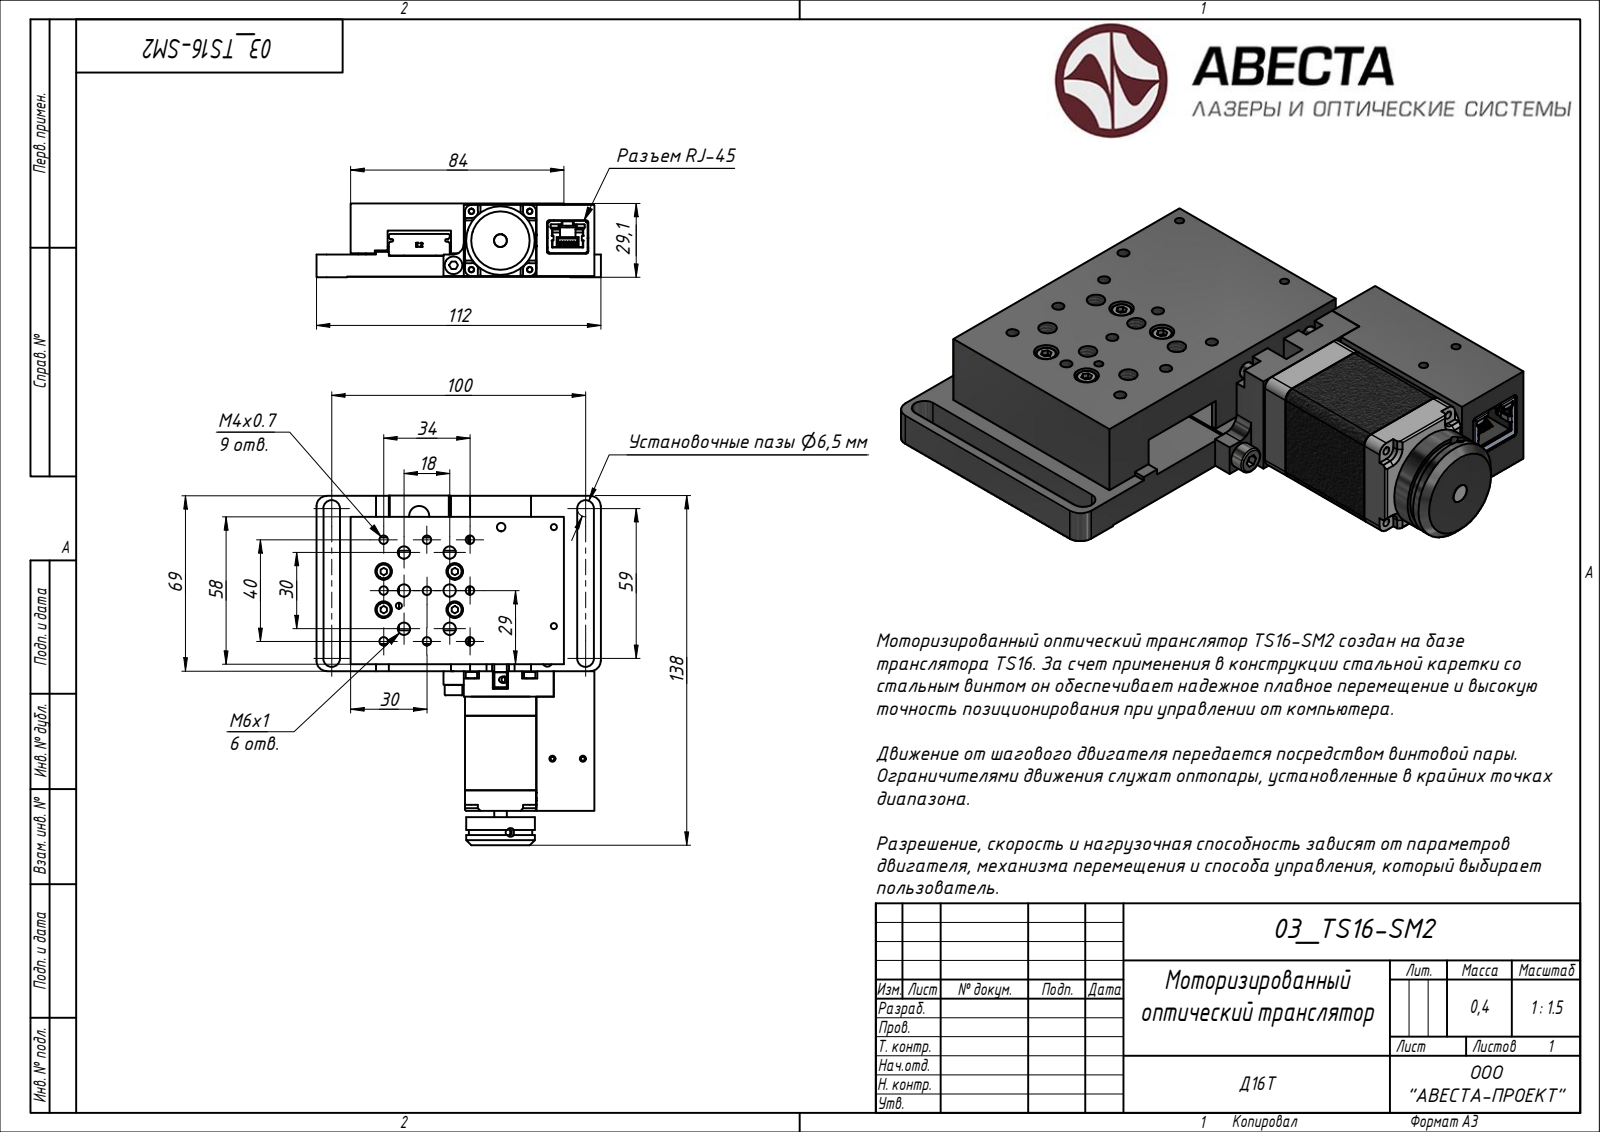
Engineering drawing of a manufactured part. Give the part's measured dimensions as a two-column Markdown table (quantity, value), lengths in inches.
| quantity | value |
| --- | --- |
| STEP written by | Rhino 7.34 (AUTOMOTIVE_DESIGN) |
| units | inches |
| bodies | 103 solids, 3067 faces (1977 planar, 803 cylindrical, 287 other) |
| overall size | 5.423 × 4.409 × 1.146 |
| volume | 12.24 in³ |
| surface area | 148.9 in² |
| round holes (diameter × count) | 0.128 × 15, 0.035 × 8, 0.097 × 7, 0.134 × 7, 0.256 × 6, 0.041 × 5, 0.097 × 5, 0.038 × 4, 0.063 × 4, 0.081 × 4, 0.087 × 4, 0.098 × 4 |
| round bosses / shafts (diameter × count) | 0.217 × 6, 0.118 × 6, 0.177 × 5, 0.098 × 5, 0.026 × 4, 0.276 × 2, 0.157 × 2, 0.15 × 2 |
| partial cylindrical surfaces (radius × count) | 0.005 × 24, 0.015 × 23, 0.007 × 19, 0.01 × 19, 0.006 × 18, 0.118 × 16, 0.039 × 13, 0.157 × 12 |
| main face-to-face distances | 0.319, 0.224, 0.335, 1.134, 0.807, 0.472, 0.661, 0.217, 1.102, 0.886 |
| hole center spacings | 0.072, 0.039, 0.08, 0.134, 0.64, 0.906, 0.079, 0.118 |
